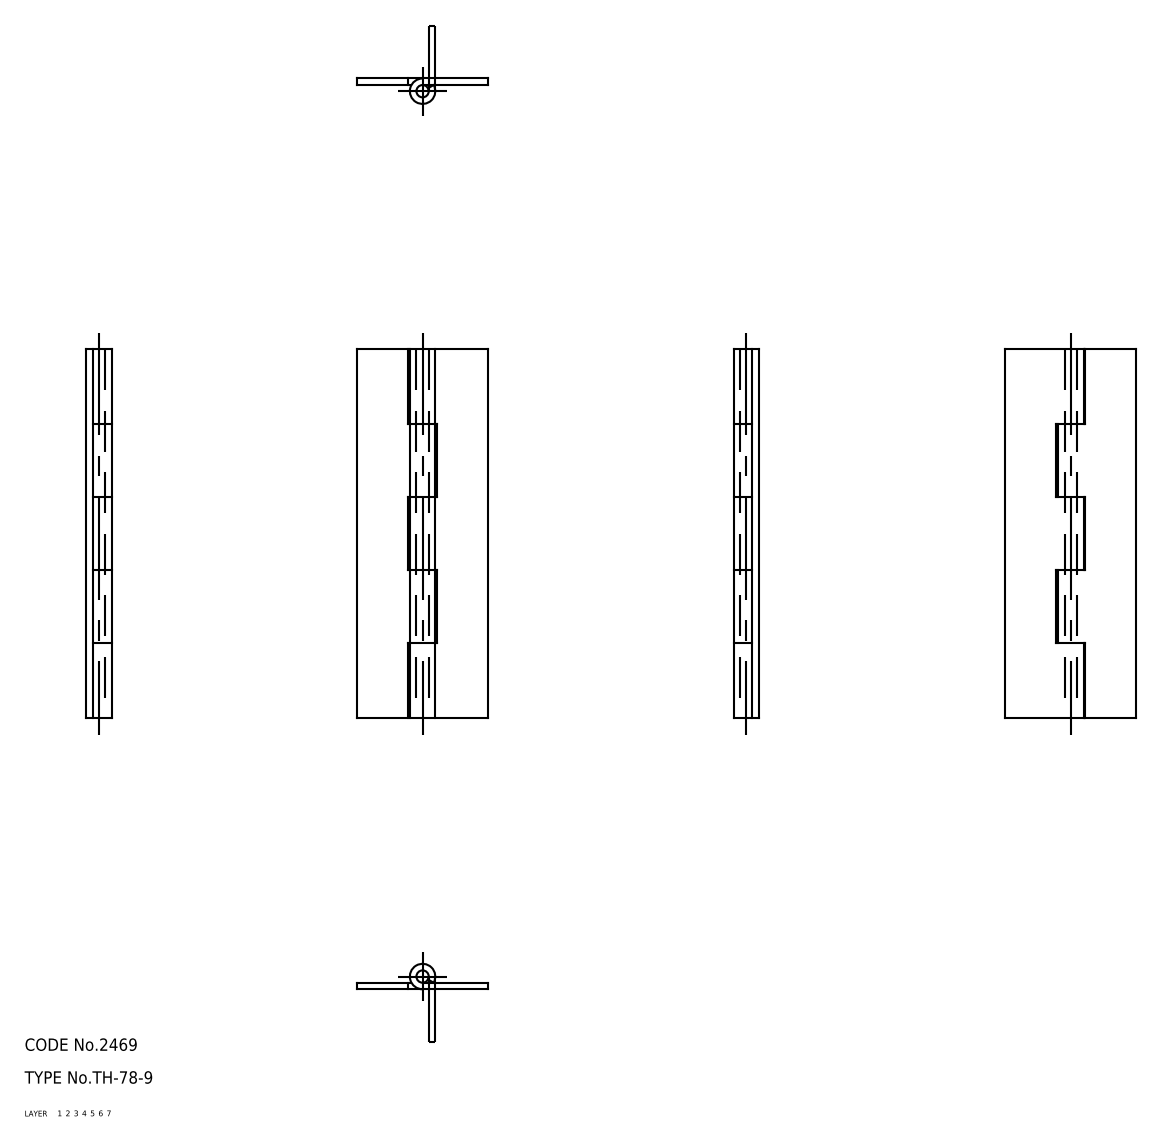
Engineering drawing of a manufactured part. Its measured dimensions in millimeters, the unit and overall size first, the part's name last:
Units: millimetres
Overall size (bounding box): 90 × 32 × 6.2
Volume: 6 464 mm³ · Surface area: 9 050 mm²
Bodies: 3 solids, 42 faces (0 planar, 0 cylindrical, 42 other)
Part name (STEP PRODUCT): hinge piece_B; hinge piece_A; shaft; TH_78_9_16981_36
STEP written by: CADfix (AUTOMOTIVE_DESIGN)
